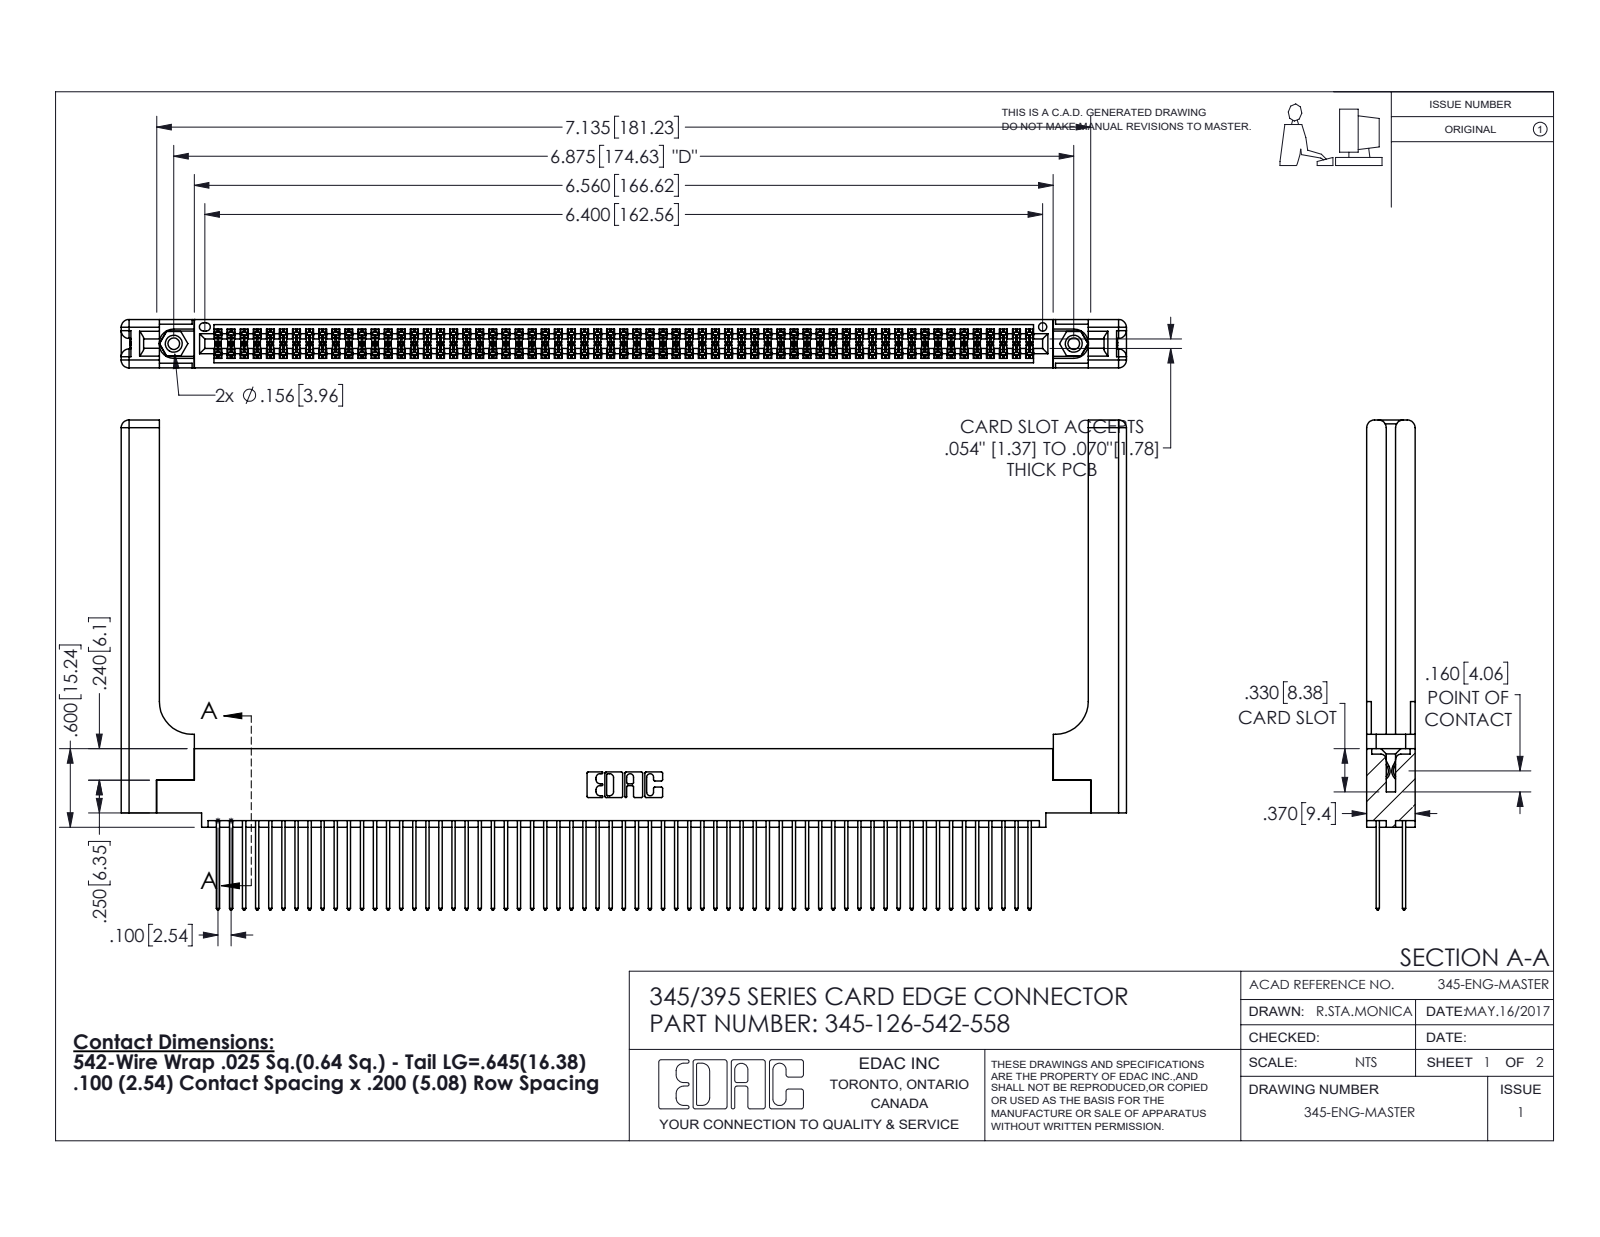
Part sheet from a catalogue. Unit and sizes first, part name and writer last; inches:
Units: inches
Overall size (bounding box): 7.679 × 3.742 × 0.37
Round holes (diameter × count): ⌀0.089 ×2, ⌀0.125 ×2, ⌀0.156 ×2, ⌀0.064 ×1
Round bosses / shafts (diameter × count): ⌀0.155 ×2
Partial cylindrical surfaces — rounded edges, fillets, slot ends (radius × count): R0.006 ×189, R0.01 ×126, R0.01 ×22, R0.06 ×16, R0.007 ×6, R0.031 ×6, R0.026 ×3, R0.014 ×2
Main face-to-face distances: 0.072, 0.298, 0.098, 0.272, 0.025, 0.2, 0.37, 0.225, 0.175, 0.148
Hole centre spacings: 0.27, 6.639, 6.875
Volume: 1.717 in³ · Surface area: 57.91 in²
Bodies: 131 solids, 6686 faces (4390 planar, 2236 cylindrical, 60 other)
Part name (STEP PRODUCT): 345-220-058_345-220-058; 345-250-001_345-250-001-102; 345 Part_0.110 Offset - 0.156 Dia-TH; 345-292-001_345-293-142 (+1 more)
STEP written by: SolidWorks 2016 (CONFIG_CONTROL_DESIGN)
